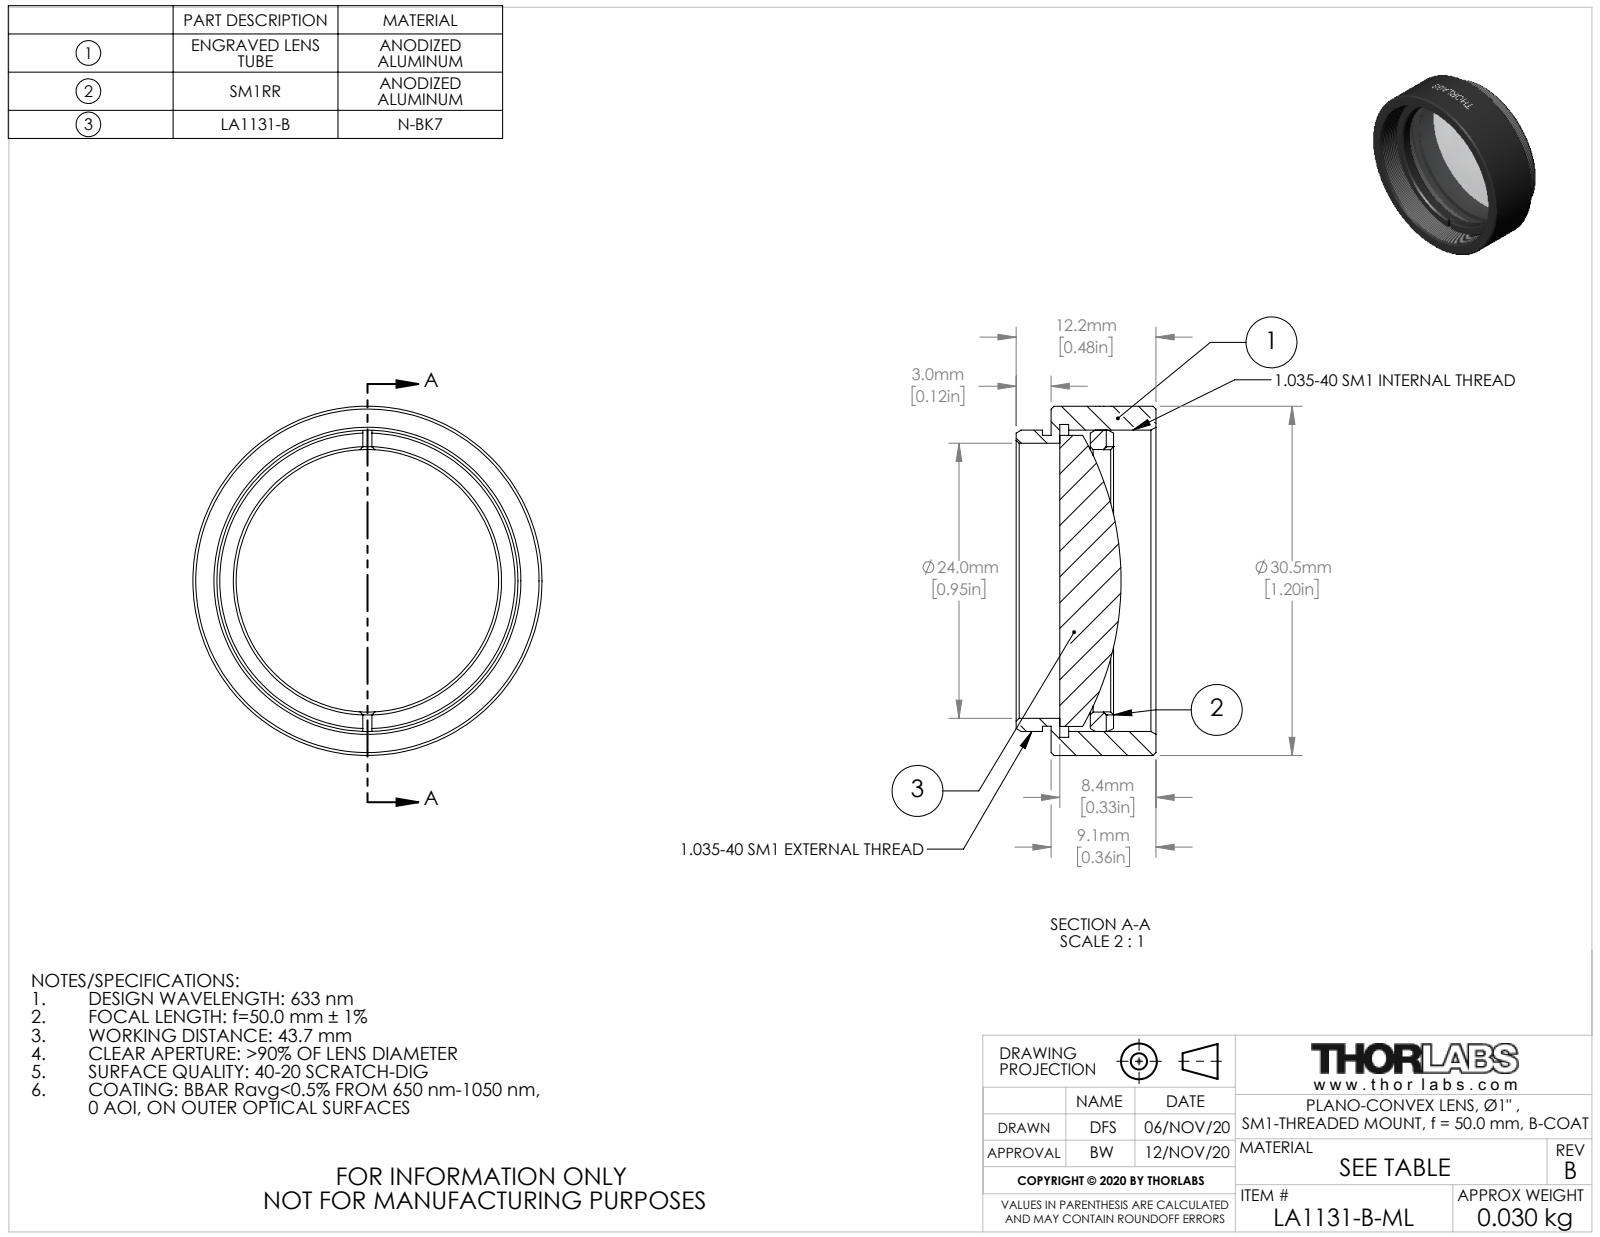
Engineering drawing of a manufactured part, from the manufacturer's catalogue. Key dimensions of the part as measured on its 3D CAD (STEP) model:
Part name (STEP PRODUCT): 24420-E0W
STEP written by: SolidWorks 2018 (CONFIG_CONTROL_DESIGN)
Units: millimetres
Bodies: 3 solids, 150 faces (20 planar, 106 cylindrical, 24 other)
Overall size (bounding box): 30.48 × 30.48 × 12.19
Volume: 4 101 mm³ · Surface area: 4 483 mm²
Round holes (diameter × count): ⌀22.91 ×1, ⌀24 ×1, ⌀26.29 ×1, ⌀27.3 ×1
Round bosses / shafts (diameter × count): ⌀30.48 ×1, ⌀26.29 ×1, ⌀25.4 ×1, ⌀25.37 ×1
Main face-to-face distances: 0.76, 9.15, 8.39, 3.42, 2.66, 5.73, 5.45, 4.69, 2.03, 3.7
